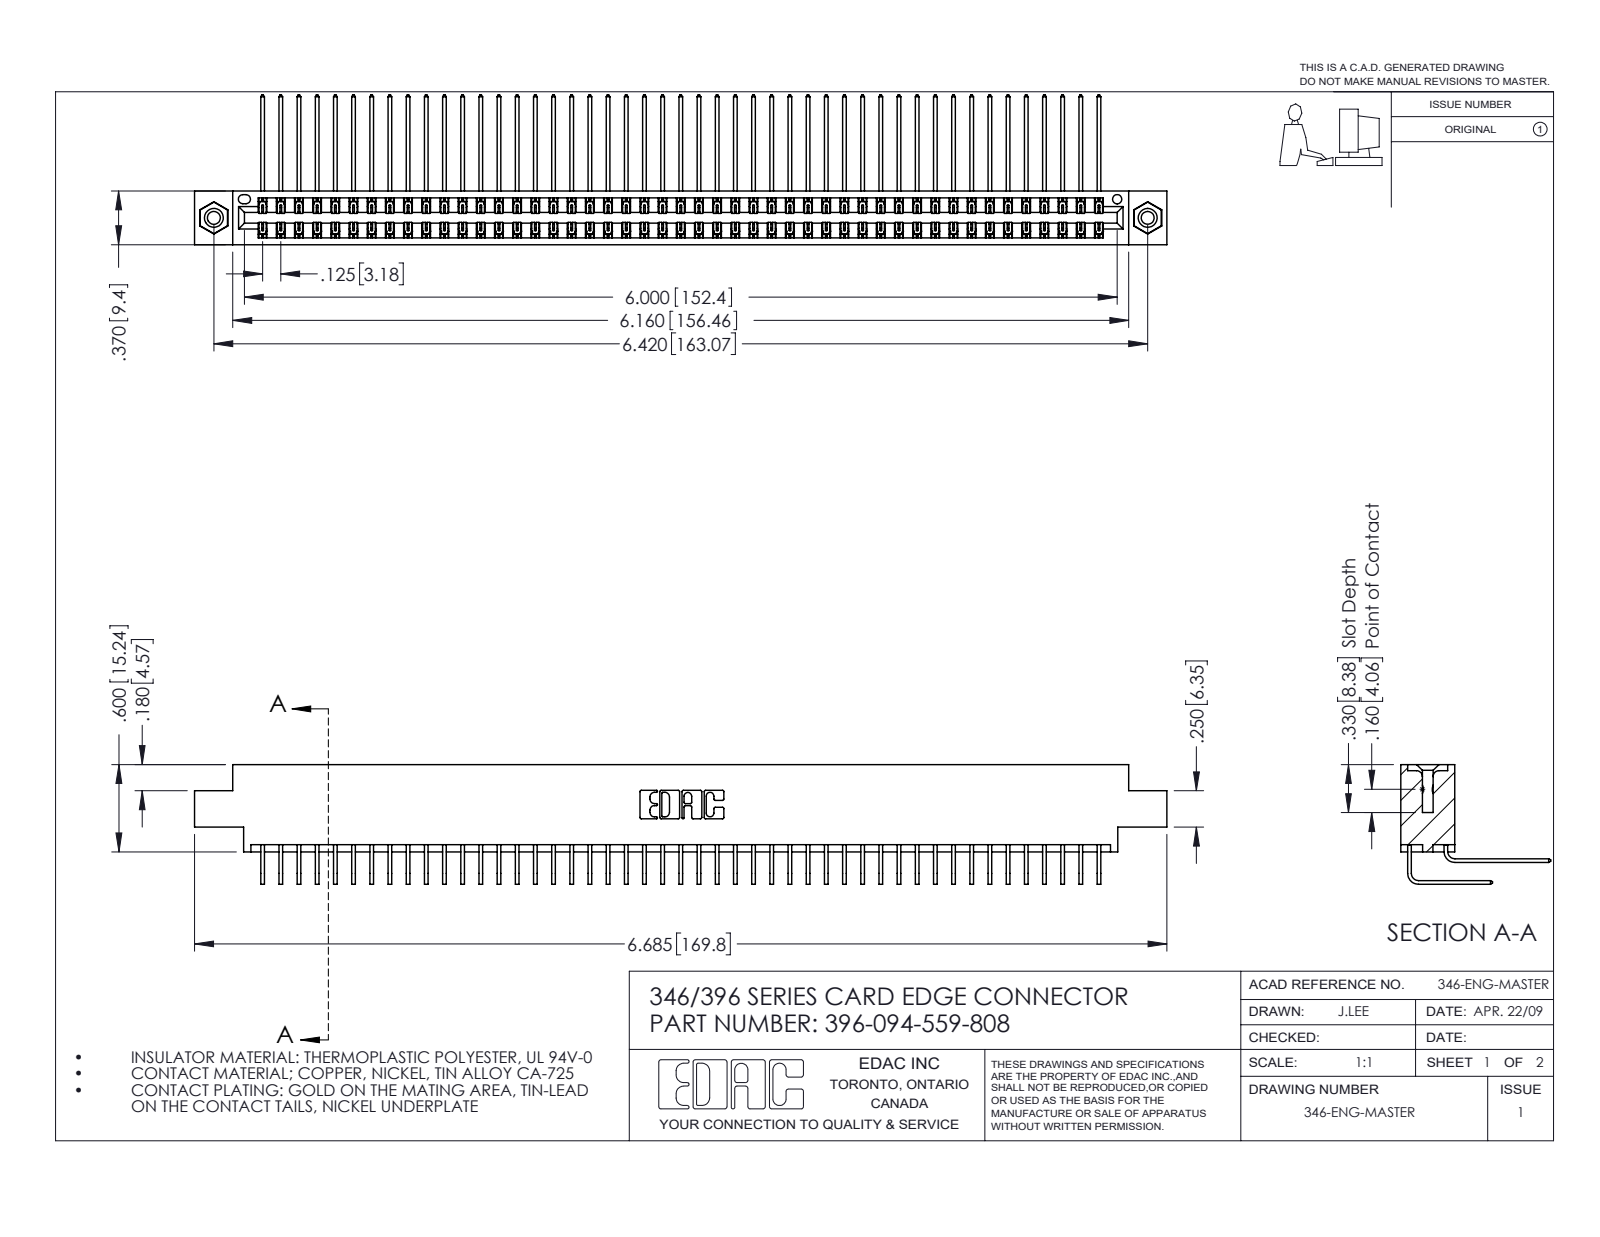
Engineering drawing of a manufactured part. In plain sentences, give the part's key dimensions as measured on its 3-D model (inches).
The part is named "345-292-001_558 559 Tail - 1; 346 Part_0.170 Offset - 0.156 Dia-TI; 345-292-001_559 Tail - 2; 345-250-001_345-250-003-102 (+1 more)". Its 3-D file was written by "SolidWorks 2016 (CONFIG_CONTROL_DESIGN)". It is 97 solids with 5262 faces: 3590 planar, 1656 cylindrical and 16 other. Overall it measures 6.685 by 1.03 by 0.823 inches. Its volume is 1.036 cubic inches and its surface area 40.64 square inches. Round holes: 2 of diameter 0.089, 2 of diameter 0.125, 2 of diameter 0.156, 1 of diameter 0.064. Round bosses or shafts: 2 of diameter 0.155. Partial cylindrical surfaces (rounded edges, fillets, slot ends): 141 of radius 0.006, 22 of radius 0.01, 6 of radius 0.007, 6 of radius 0.031, 3 of radius 0.026, 2 of radius 0.014, 2 of radius 0.022, 2 of radius 0.024. The main face-to-face distances are 0.048, 0.322, 0.025, 0.37, 0.25, 0.072, 0.298, 0.275, 0.222, 0.148. The hole center spacings are 0.246, 6.211, 6.42.
